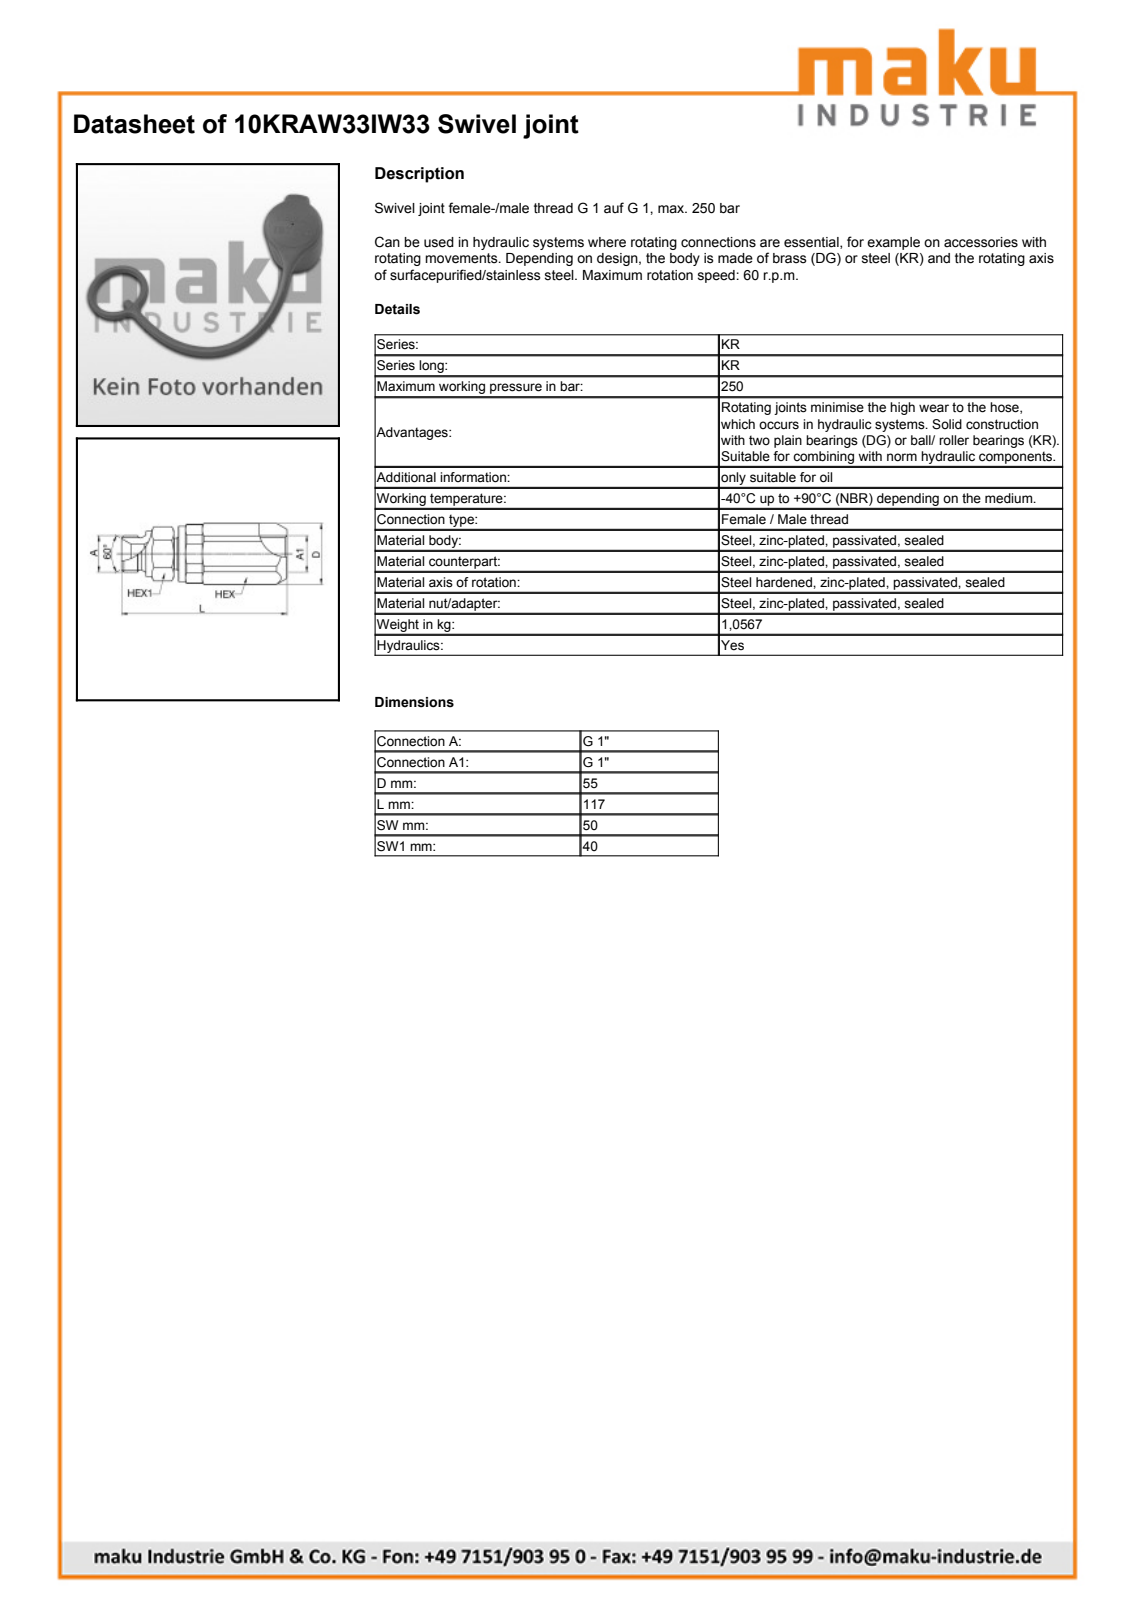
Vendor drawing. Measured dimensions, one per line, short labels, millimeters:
name: 10KRAW33IW33
written by: SolidWorks 2009 (AUTOMOTIVE_DESIGN)
unit: mm
bodies: 1 solid, 130 faces (36 planar, 34 cylindrical, 60 other)
size: 117.2 × 55 × 50
volume: 148 814 mm³; area: 31 179 mm²
holes: 1× ⌀22, 1× ⌀26, 1× ⌀30.2, 1× ⌀30.29, 1× ⌀37
bosses: 1× ⌀49.6, 1× ⌀39, 1× ⌀33.25, 1× ⌀29.9, 1× ⌀29
rounds: 1× R27.5
face distances: 50, 5, 45, 40, 73.2, 75.2, 2, 72.15, 1.05, 3.05
